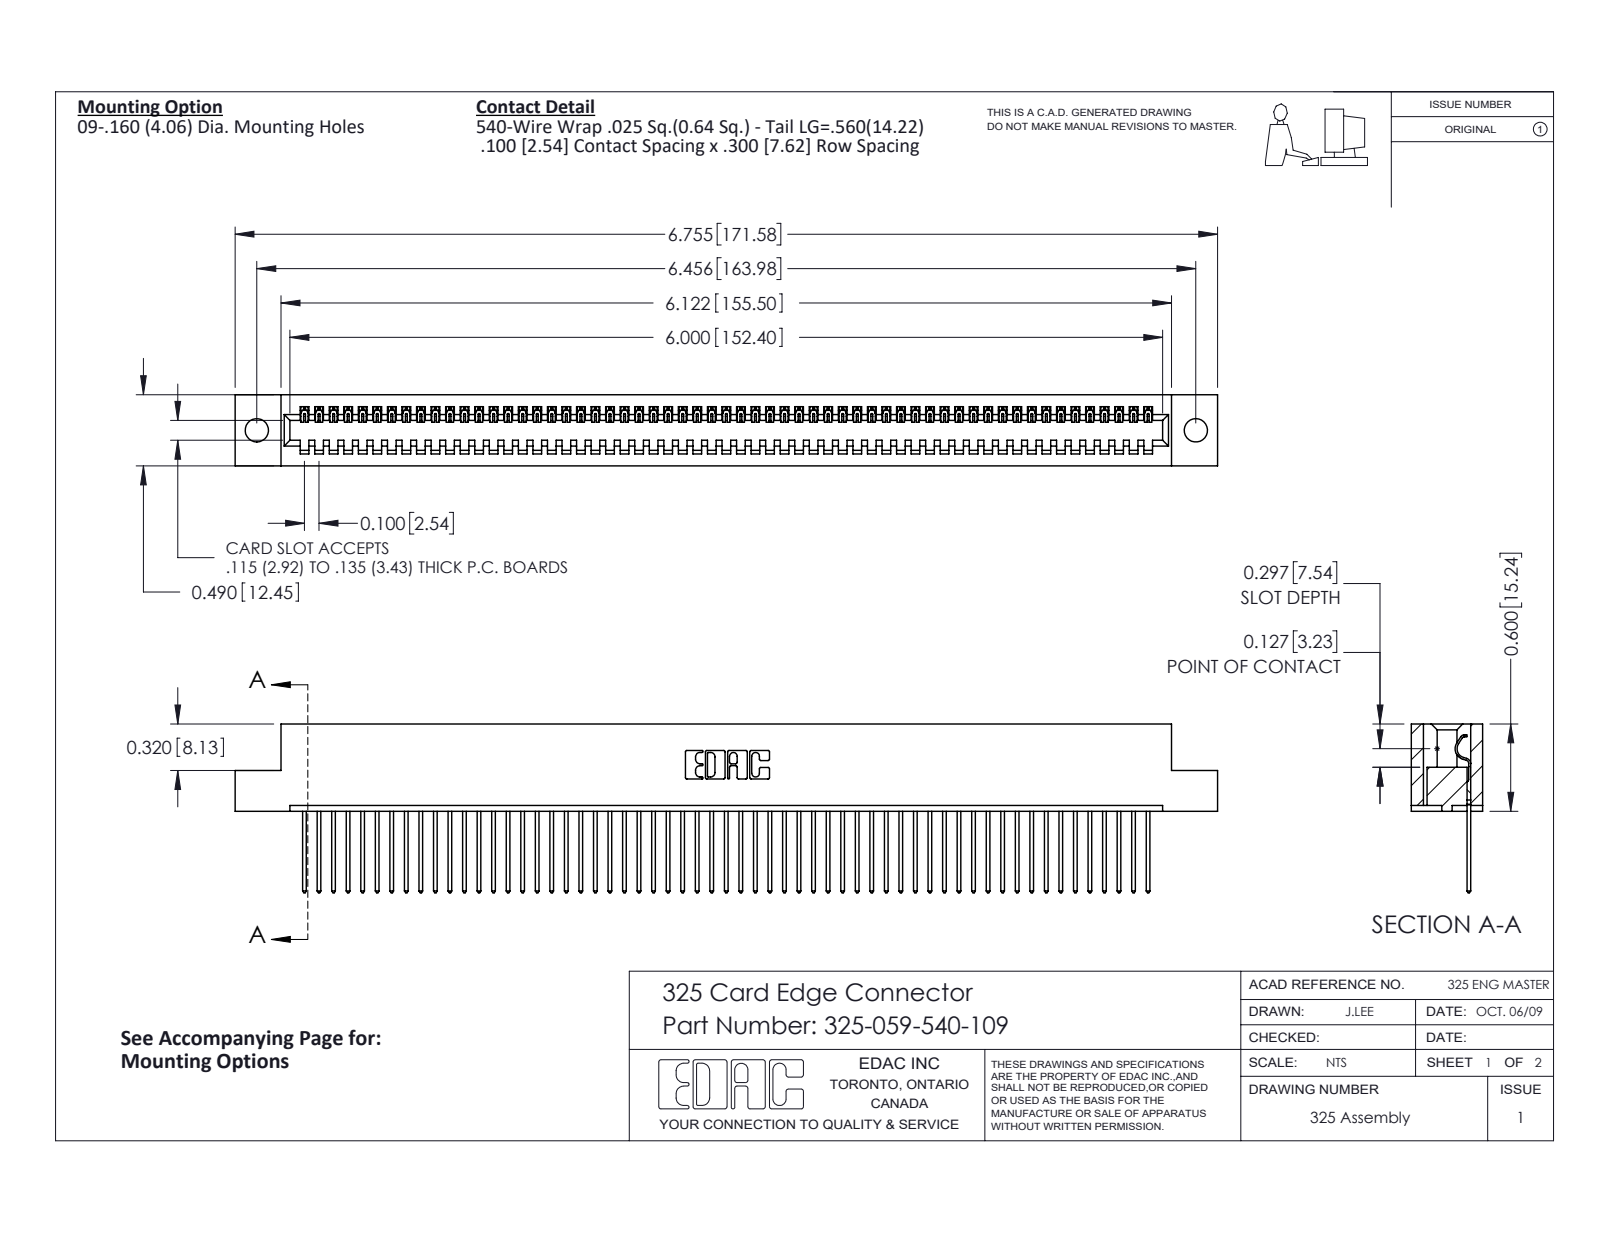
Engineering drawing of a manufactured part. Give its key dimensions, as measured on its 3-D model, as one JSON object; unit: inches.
{"part_name": "325 Part_.160 TH; 325-059-540-109; 325-292-001_325-293-140", "step_written_by": "SolidWorks 2016 (CONFIG_CONTROL_DESIGN)", "units": "inches", "bodies": {"solids": 60, "faces": 3536, "planar": 2548, "cylindrical": 988, "other": 0}, "overall_size": [6.755, 1.16, 0.49], "volume_in3": 1.328, "surface_area_in2": 38.06, "round_holes": [[0.16, 2]], "partial_cylinders_radius": [[0.006, 118], [0.01, 118], [0.01, 22], [0.007, 6], [0.031, 6], [0.026, 3], [0.014, 1], [0.022, 1]], "face_to_face_distances": [0.083, 0.407, 0.3, 0.49, 0.107, 0.383, 0.025, 0.325, 0.56, 0.263], "hole_center_spacings": [6.456]}
